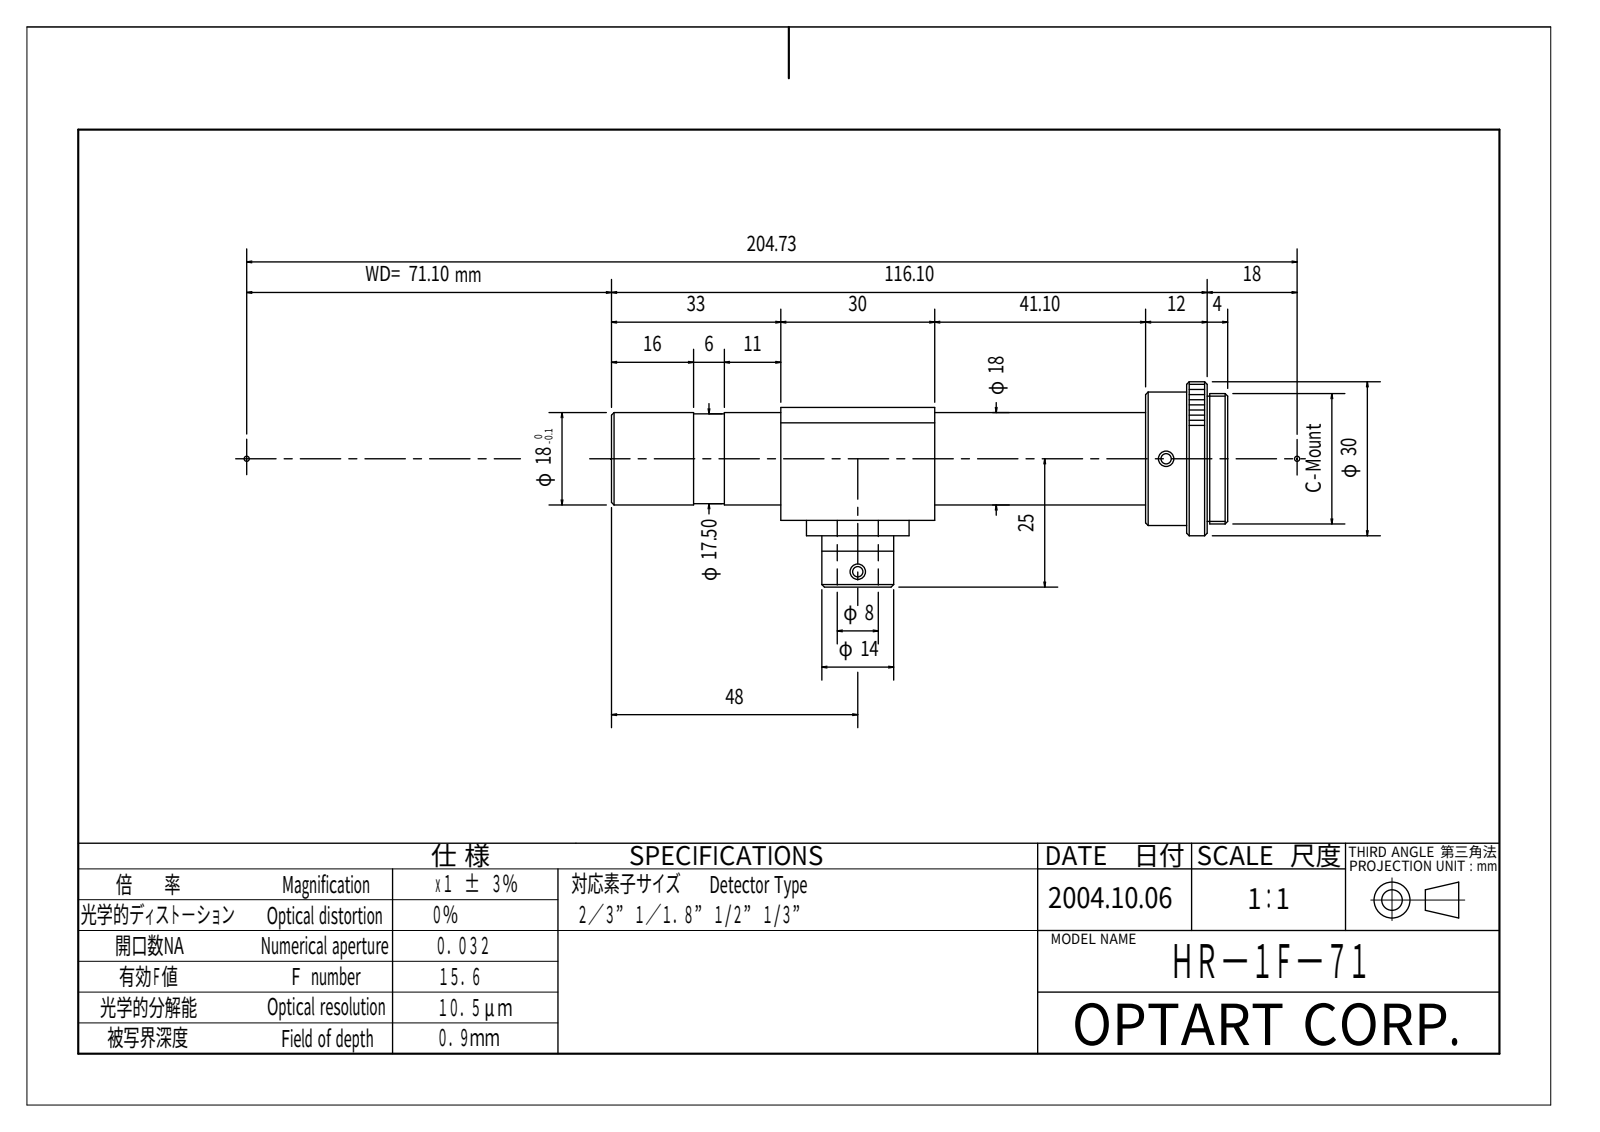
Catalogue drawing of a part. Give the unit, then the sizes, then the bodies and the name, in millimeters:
Units: millimetres
Overall size (bounding box): 120.4 × 40 × 30
Round holes (diameter × count): ⌀8 ×1, ⌀11.5 ×1, ⌀12 ×1, ⌀14.5 ×1, ⌀15 ×1, ⌀16.5 ×1
Round bosses / shafts (diameter × count): ⌀3.5 ×4, ⌀30 ×1, ⌀26 ×1, ⌀25.4 ×1, ⌀24.6 ×1, ⌀20 ×1, ⌀18 ×1, ⌀17.5 ×1
Main face-to-face distances: 20, 25, 22, 3, 6, 4, 10, 8, 16, 12
Volume: 41 230 mm³ · Surface area: 12 489 mm²
Bodies: 6 solids, 134 faces (44 planar, 46 cylindrical, 44 other)
Part name (STEP PRODUCT): HR-1F-71 3D-Data
STEP written by: SolidWorks 2016 (AUTOMOTIVE_DESIGN)
